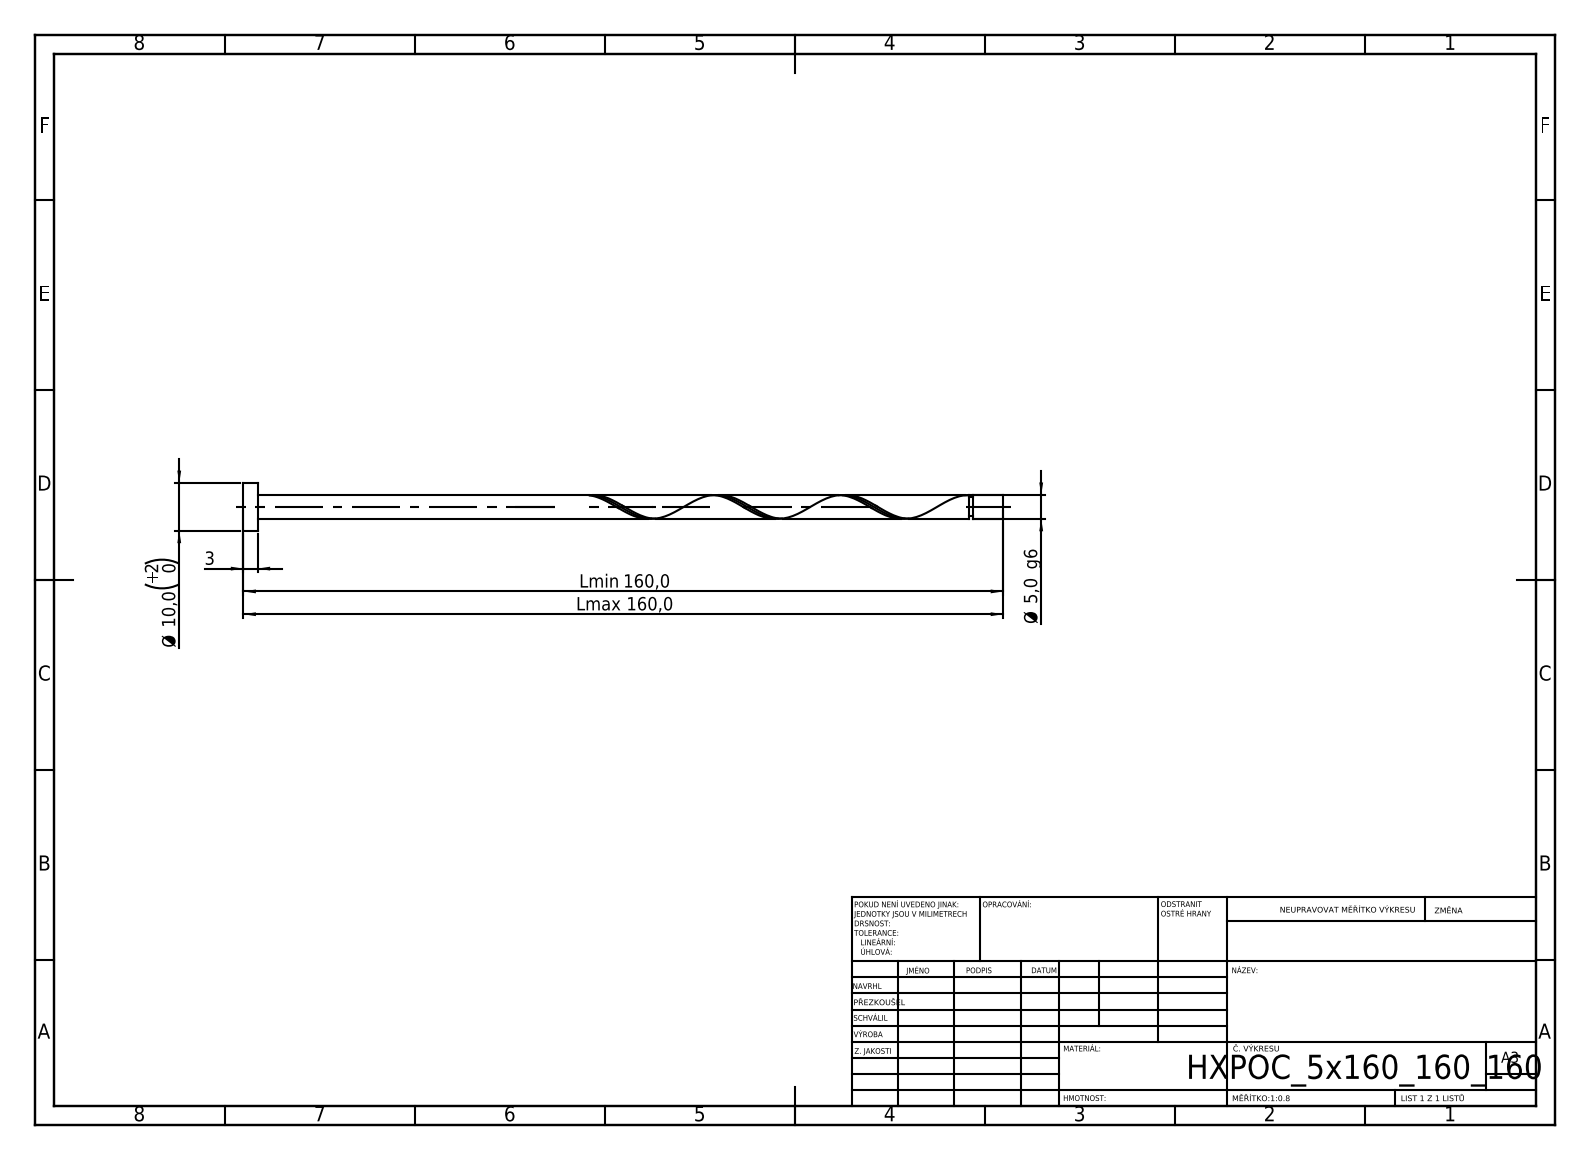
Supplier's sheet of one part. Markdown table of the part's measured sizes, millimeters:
| quantity | value |
| --- | --- |
| STEP written by | SolidWorks 2019 (CONFIG_CONTROL_DESIGN) |
| units | millimeters |
| bodies | 1 solid, 21 faces (6 planar, 14 cylindrical, 1 other) |
| overall size | 160 × 10 × 10 |
| volume | 3 281 mm³ |
| surface area | 2 775 mm² |
| round bosses / shafts (diameter × count) | 10 × 1, 5 × 1, 4 × 1 |
| main face-to-face distances | 3, 160, 157, 153.74, 150.74, 6.26, 152.74, 149.74, 1, 7.26 |
